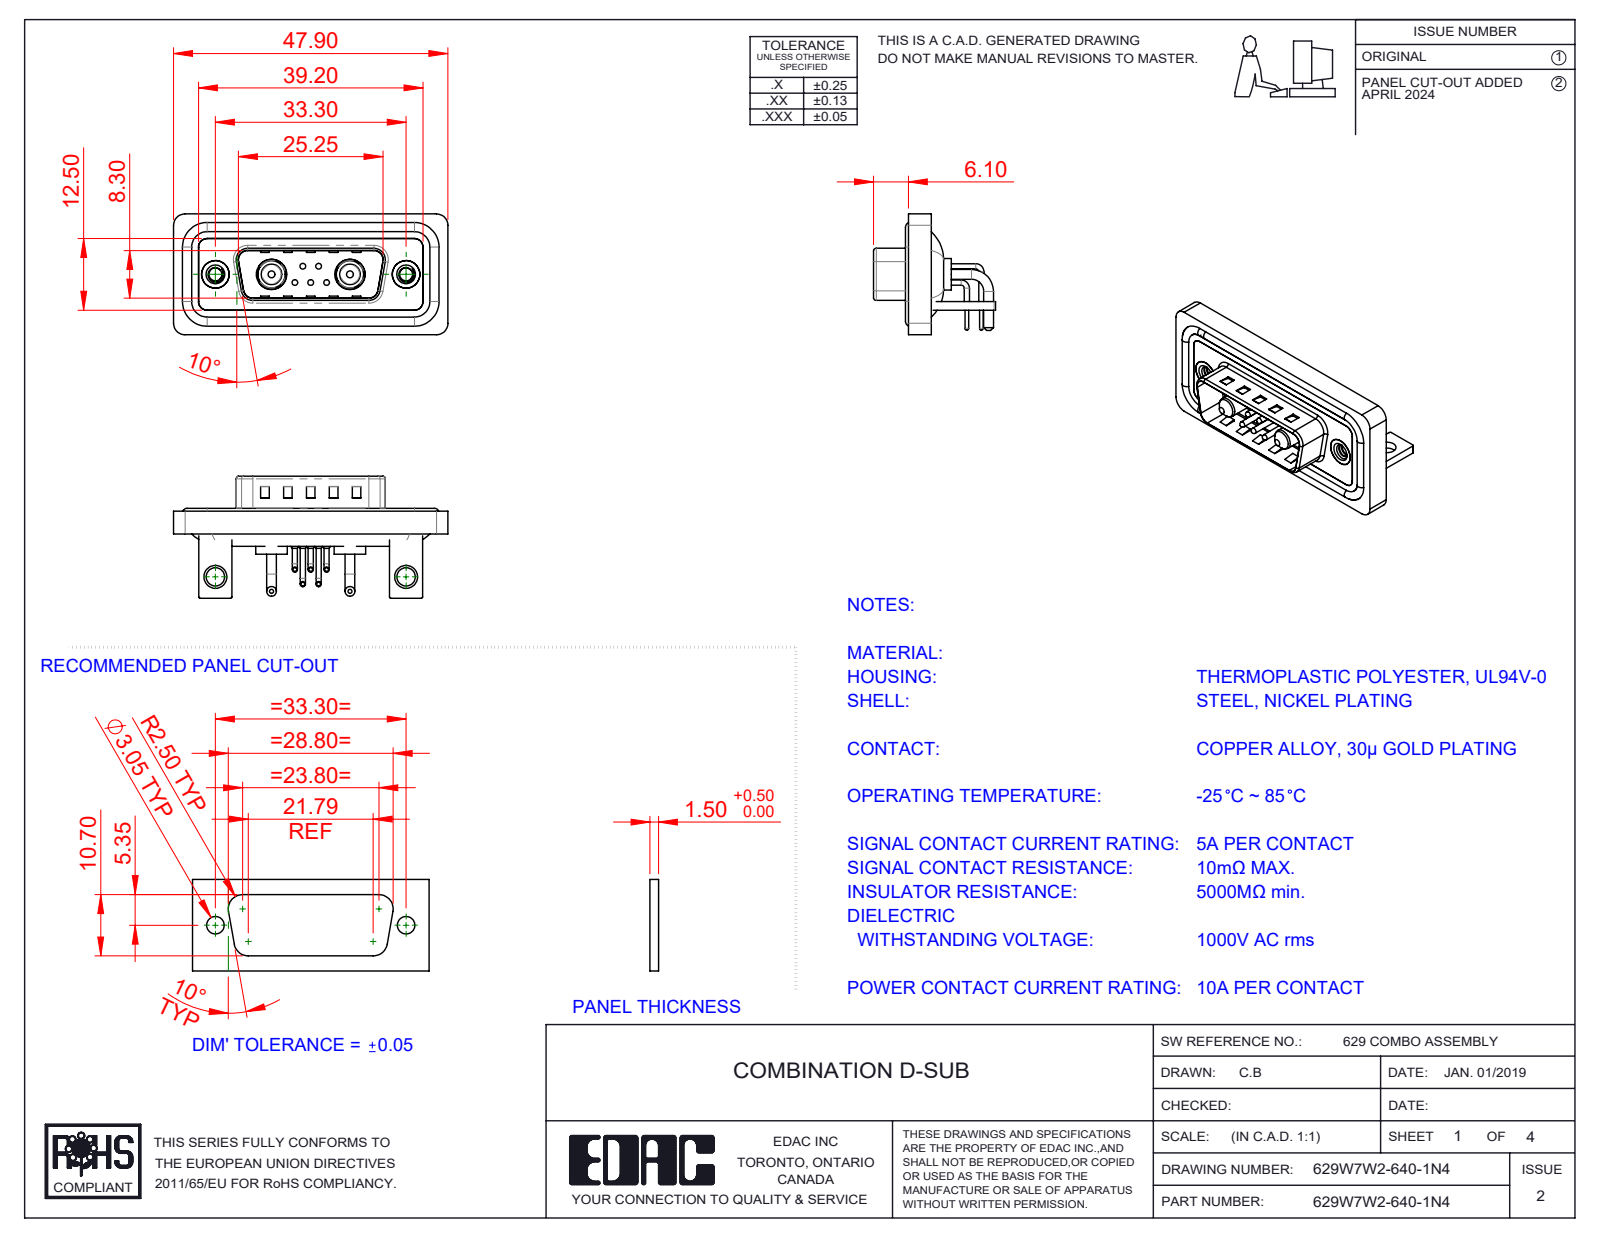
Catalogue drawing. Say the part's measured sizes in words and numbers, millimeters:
The part is named "Power Pin_10A RA; 629W7W2-640-1N4; 629Combo Threaded Rivet_3; 629Combo Housing_7W2 (+6 more)". Its 3-D file was written by "SolidWorks 2023 (CONFIG_CONTROL_DESIGN)". It is 18 solids with 1123 faces: 537 planar, 424 cylindrical and 162 other. Overall it measures 47.9 by 21.3 by 21.1 millimeters. Its volume is 5 842 cubic millimeters and its surface area 9 626 square millimeters. Round holes: 5 of diameter 0.75, 5 of diameter 1.6, 5 of diameter 2, 2 of diameter 2.26, 2 of diameter 3.2, 2 of diameter 4, 2 of diameter 4.8, 2 of diameter 4.85, 2 of diameter 5, 2 of diameter 5.3. Round bosses or shafts: 10 of diameter 0.9, 5 of diameter 1.5, 5 of diameter 1, 5 of diameter 0.65, 4 of diameter 1.7, 4 of diameter 1.6, 2 of diameter 5.5, 2 of diameter 5.2. Partial cylindrical surfaces (rounded edges, fillets, slot ends): 21 of radius 2, 18 of radius 1.5, 16 of radius 0.25, 9 of radius 0.5, 8 of radius 1.6, 5 of radius 1.01, 4 of radius 0.6, 4 of radius 0.65. The main face-to-face distances are 0.4, 1.5, 0.8, 2.9, 2.1, 1.1, 1.6, 1.2, 3.7, 4.5. The hole center spacings are 3.16, 2.77, 9.8, 23.5, 33.3, 4.31, 4.33, 5.03.
